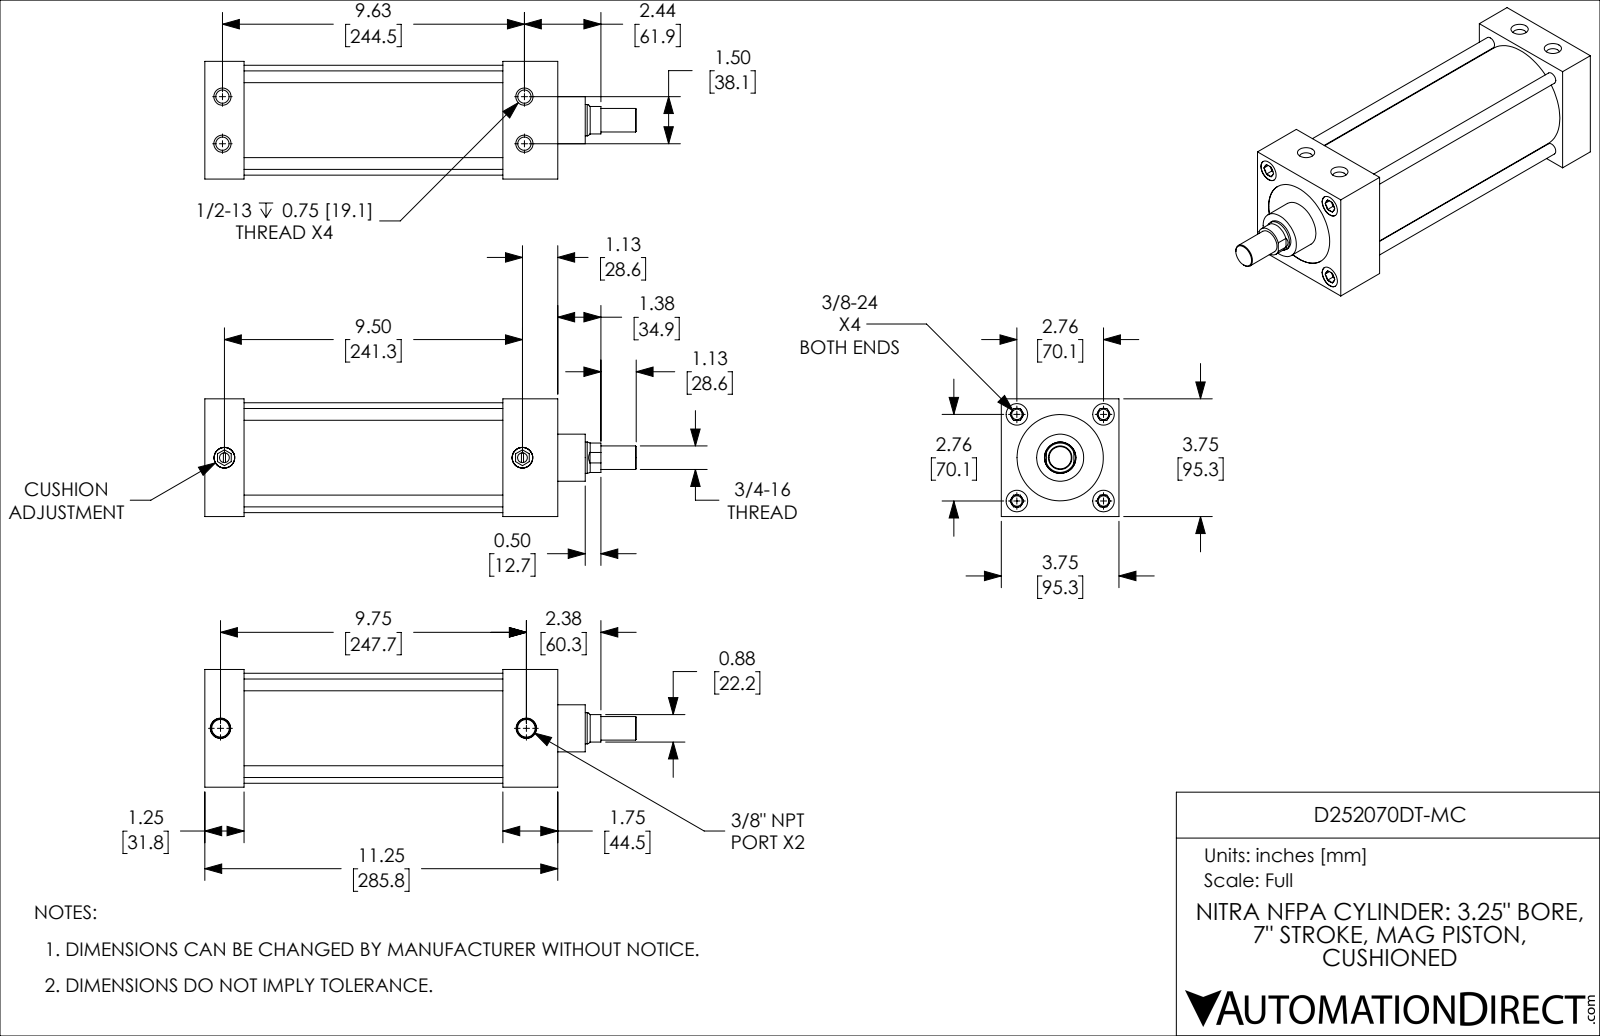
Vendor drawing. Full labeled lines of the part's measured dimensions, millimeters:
Part name (STEP PRODUCT): D252070DT-MC_PISTON_KK1; D252070DT-MC_CUSHION; D252070DT-MC_BODY; D252070DT-MC
STEP written by: SolidWorks 2019 (CONFIG_CONTROL_DESIGN)
Units: millimetres
Bodies: 4 solids, 246 faces (90 planar, 78 cylindrical, 78 other)
Overall size (bounding box): 349.3 × 95.3 × 95.3
Volume: 1 191 000 mm³ · Surface area: 264 000 mm²
Round holes (diameter × count): ⌀8.4 ×4, ⌀10.7 ×4, ⌀17.4 ×4, ⌀7.9 ×2, ⌀14.3 ×2, ⌀16.7 ×2, ⌀25.4 ×1, ⌀69.9 ×1, ⌀82.6 ×1
Round bosses / shafts (diameter × count): ⌀9.5 ×4, ⌀16.7 ×2, ⌀88.9 ×1, ⌀82.5 ×1, ⌀38.1 ×1, ⌀25.4 ×1, ⌀19.1 ×1
Partial cylindrical surfaces — rounded edges, fillets, slot ends (radius × count): R11.9 ×1
Main face-to-face distances: 31.8, 95.3, 241.3, 209.6, 63.5, 177.8, 285.8, 254, 222.3, 44.5
Hole centre spacings: 19.1, 49.6, 70.1, 246.8, 38.1, 99.1, 244.5, 247.4
